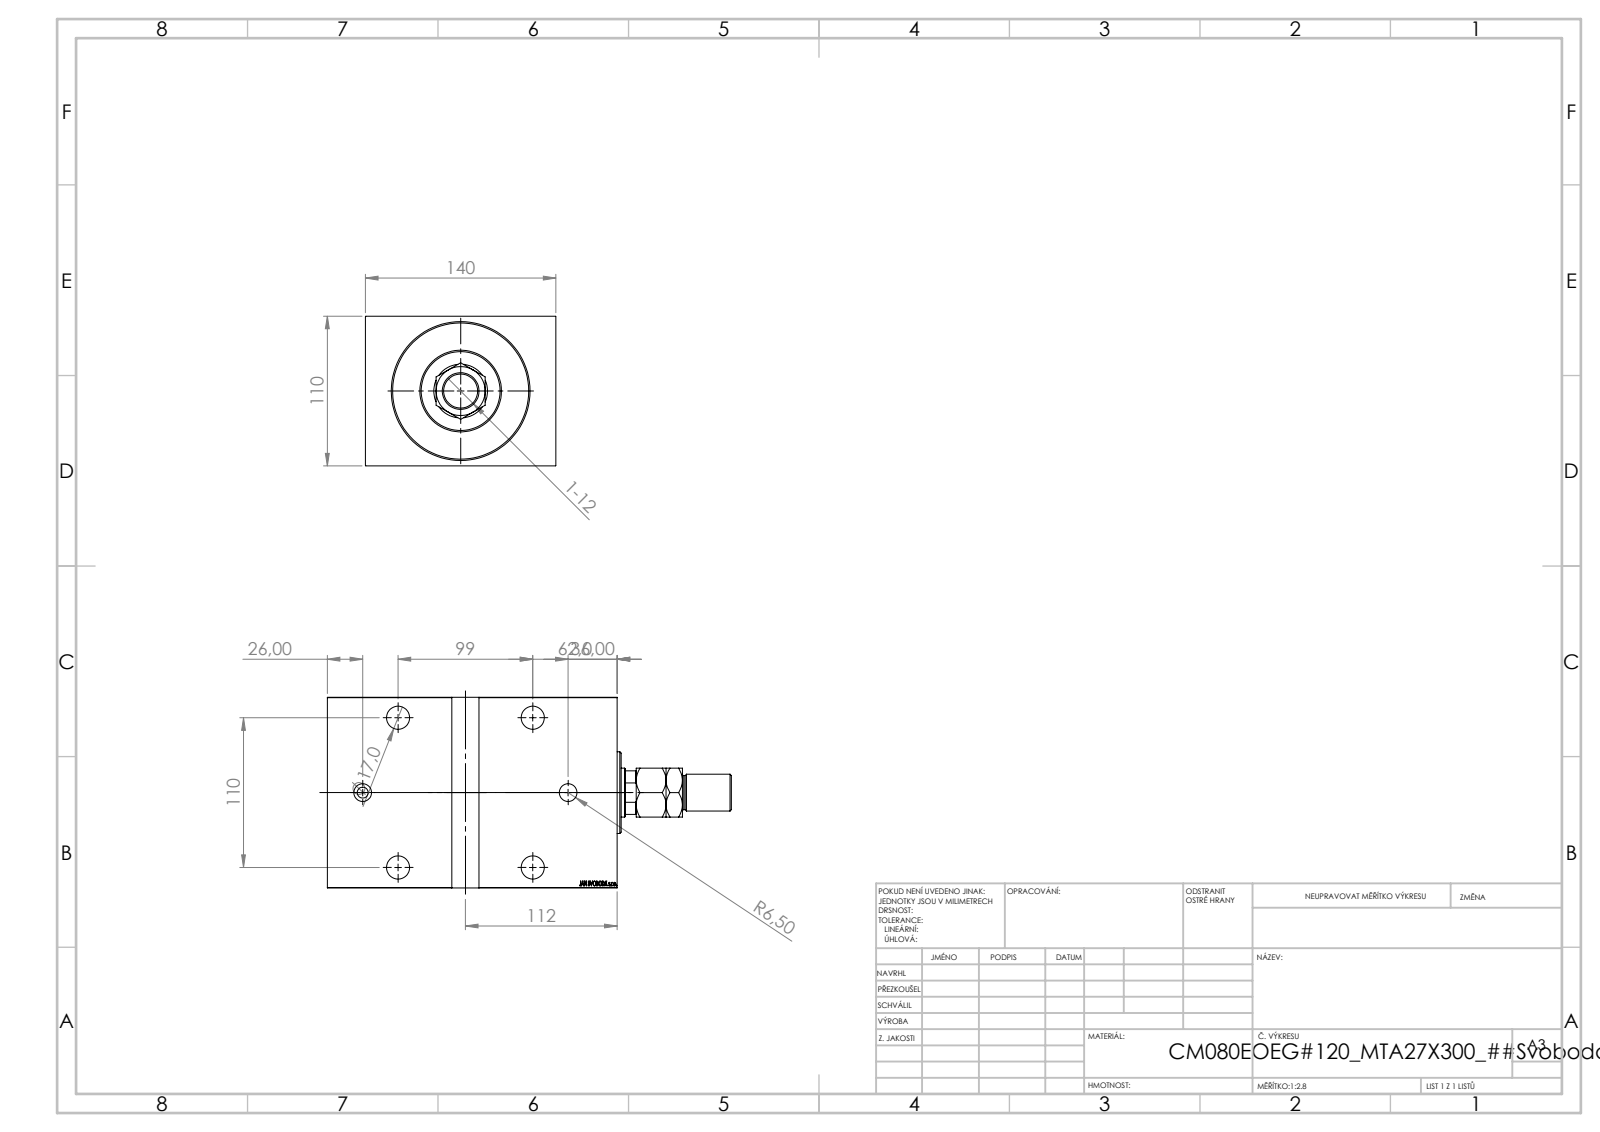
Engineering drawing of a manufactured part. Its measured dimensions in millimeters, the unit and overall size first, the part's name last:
Units: millimetres
Overall size (bounding box): 297 × 140 × 110
Round holes (diameter × count): ⌀17 ×4, ⌀25 ×4, ⌀13 ×2, ⌀25.5 ×1, ⌀36 ×1, ⌀39.5 ×1, ⌀80 ×1, ⌀100 ×1
Round bosses / shafts (diameter × count): ⌀82 ×1, ⌀60 ×1, ⌀27 ×1, ⌀25 ×1, ⌀8 ×1
Partial cylindrical surfaces — rounded edges, fillets, slot ends (radius × count): R17.5 ×1
Main face-to-face distances: 110, 140, 213, 21, 192, 5, 208, 187, 79, 196.4
Hole centre spacings: 60.84, 136.57, 99, 110, 147.99, 151
Volume: 2 730 000 mm³ · Surface area: 285 590 mm²
Bodies: 4 solids, 898 faces (424 planar, 50 cylindrical, 424 other)
Part name (STEP PRODUCT): V450CM_E_Body; MTA; V450CM_E_VCP; V450CM_VC_B
STEP written by: SolidWorks 2019 (CONFIG_CONTROL_DESIGN)
